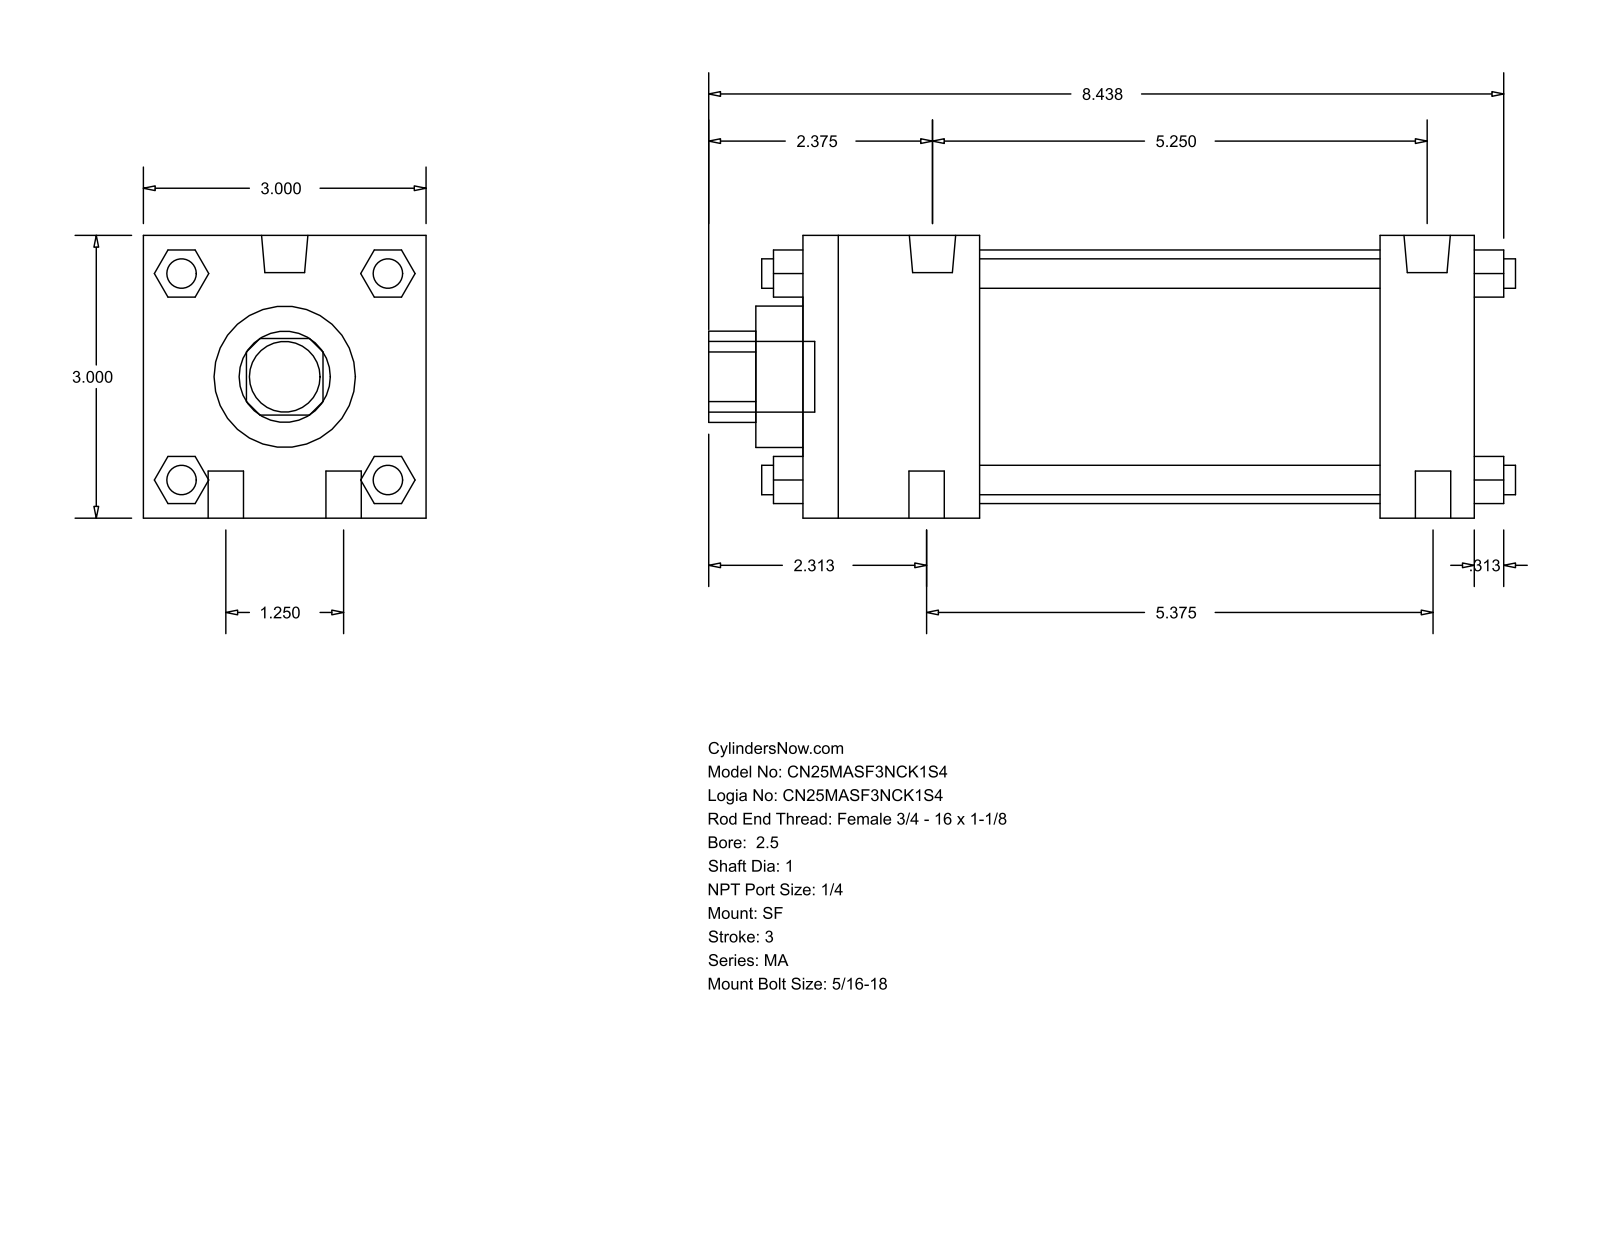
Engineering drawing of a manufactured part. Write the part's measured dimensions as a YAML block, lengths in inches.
part_name: "MA_SF__0250_1"
step_written_by: "GSSL Pune (CONFIG_CONTROL_DESIGN)"
units: inches
bodies: {solids: 0, faces: 124, planar: 94, cylindrical: 30, other: 0}
overall_size: [8.563, 3, 3]
round_holes:
  - {diameter: 1, count: 1}
  - {diameter: 1.5, count: 1}
  - {diameter: 2.69, count: 1}
round_bosses_or_shafts:
  - {diameter: 0.313, count: 6}
  - {diameter: 0.375, count: 4}
  - {diameter: 0.492, count: 2}
  - {diameter: 0.75, count: 1}
partial_cylinders:
  - {radius: 0.484, count: 1}
face_to_face_distances: [3, 7.125, 0.5, 6.125, 1, 1.875, 4.25, 5.25, 1.095, 1.896]
